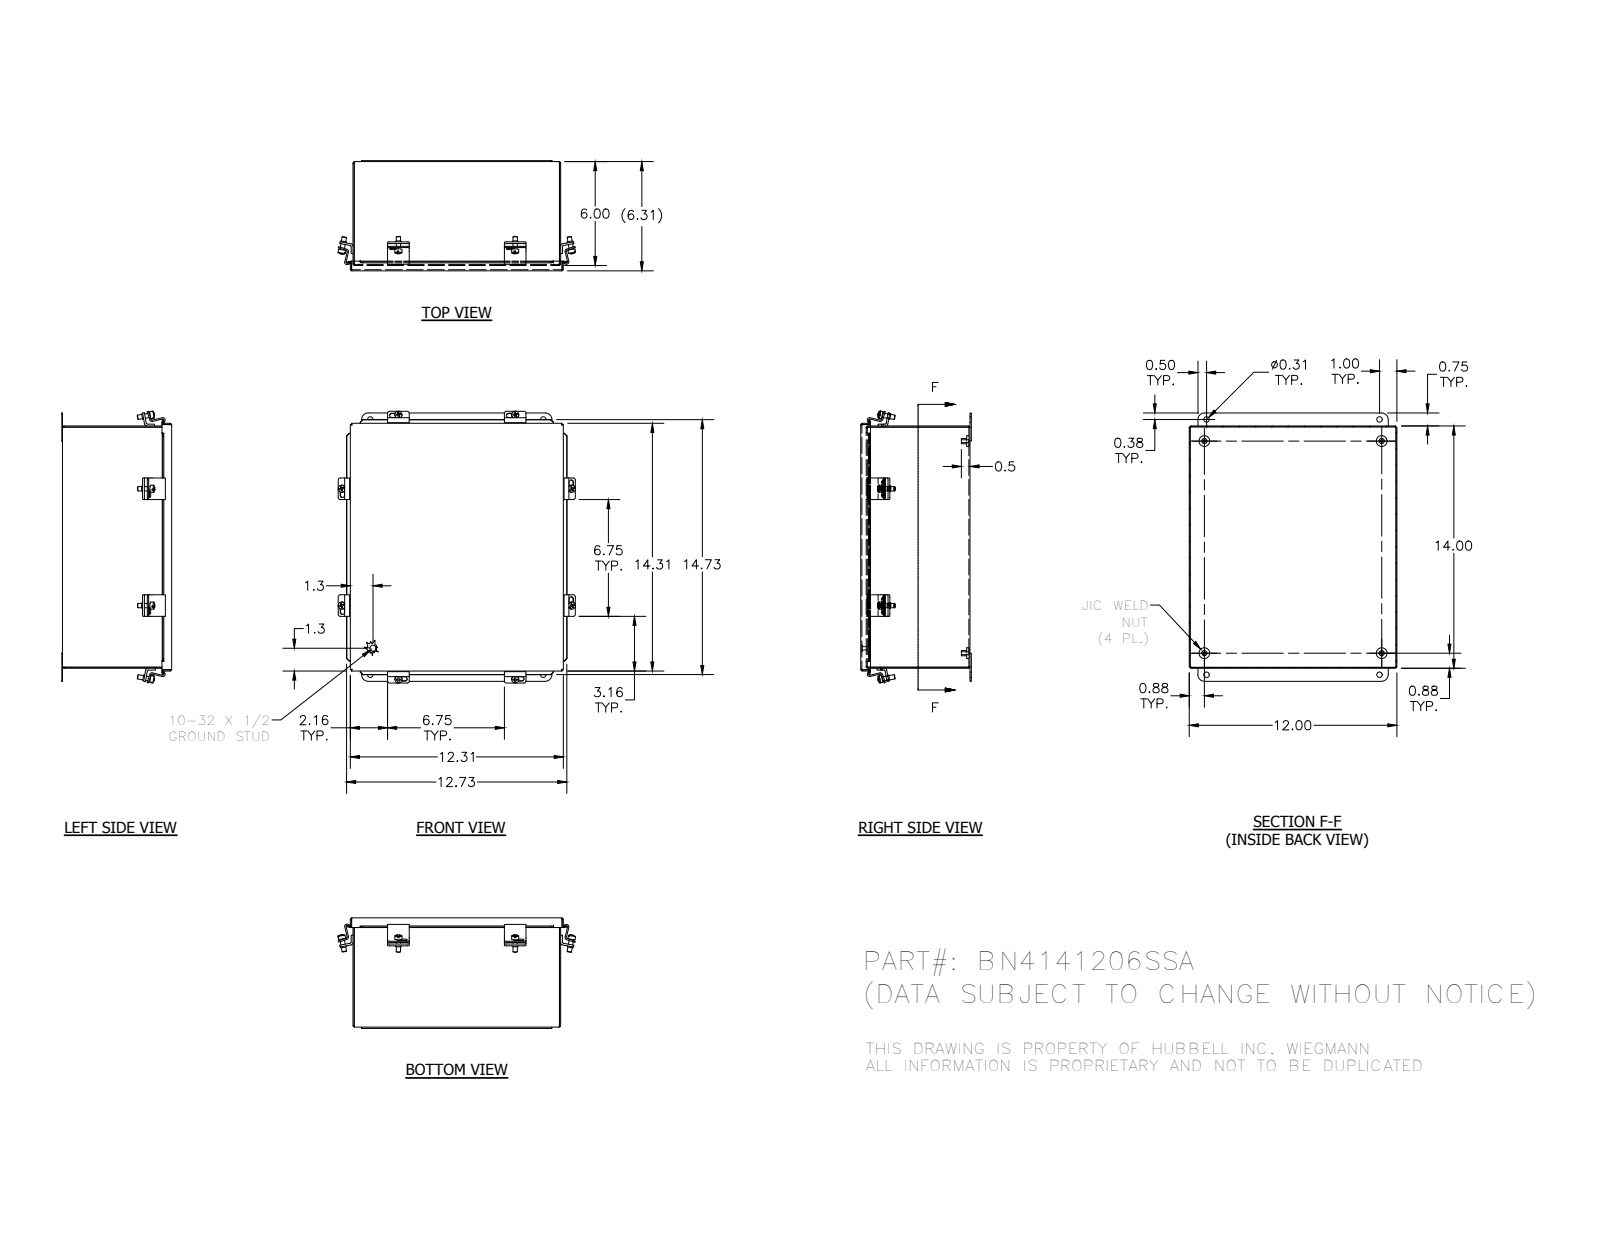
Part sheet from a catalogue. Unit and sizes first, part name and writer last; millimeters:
Units: millimetres
Overall size (bounding box): 399.1 × 348.6 × 162.3
Round holes (diameter × count): ⌀2.8 ×12, ⌀5 ×8, ⌀4 ×4, ⌀7.9 ×4
Round bosses / shafts (diameter × count): ⌀10.4 ×8, ⌀8.7 ×8, ⌀6.4 ×8, ⌀15.9 ×4, ⌀7.6 ×4, ⌀8.6 ×1, ⌀4.8 ×1
Partial cylindrical surfaces — rounded edges, fillets, slot ends (radius × count): R3.2 ×32, R0.8 ×16, R2.4 ×16, R3.4 ×16, R1.6 ×12, R3.2 ×12, R9.5 ×4
Main face-to-face distances: 1.6, 158.8, 160.4, 157.1, 303.2, 354, 304.8, 301.6, 355.6, 352.4
Hole centre spacings: 171.5, 19.1, 1.6, 19.1, 31.9, 171.5, 342.9, 152.4
Volume: 806 700 mm³ · Surface area: 1 003 000 mm²
Bodies: 33 solids, 917 faces (439 planar, 328 cylindrical, 150 other)
Part name (STEP PRODUCT): BN4141206SSABKP_1; BN41412SSALID_1; HFW3883_1; 34973_1 (+5 more)
STEP written by: SolidWorks 2014 (AUTOMOTIVE_DESIGN)
